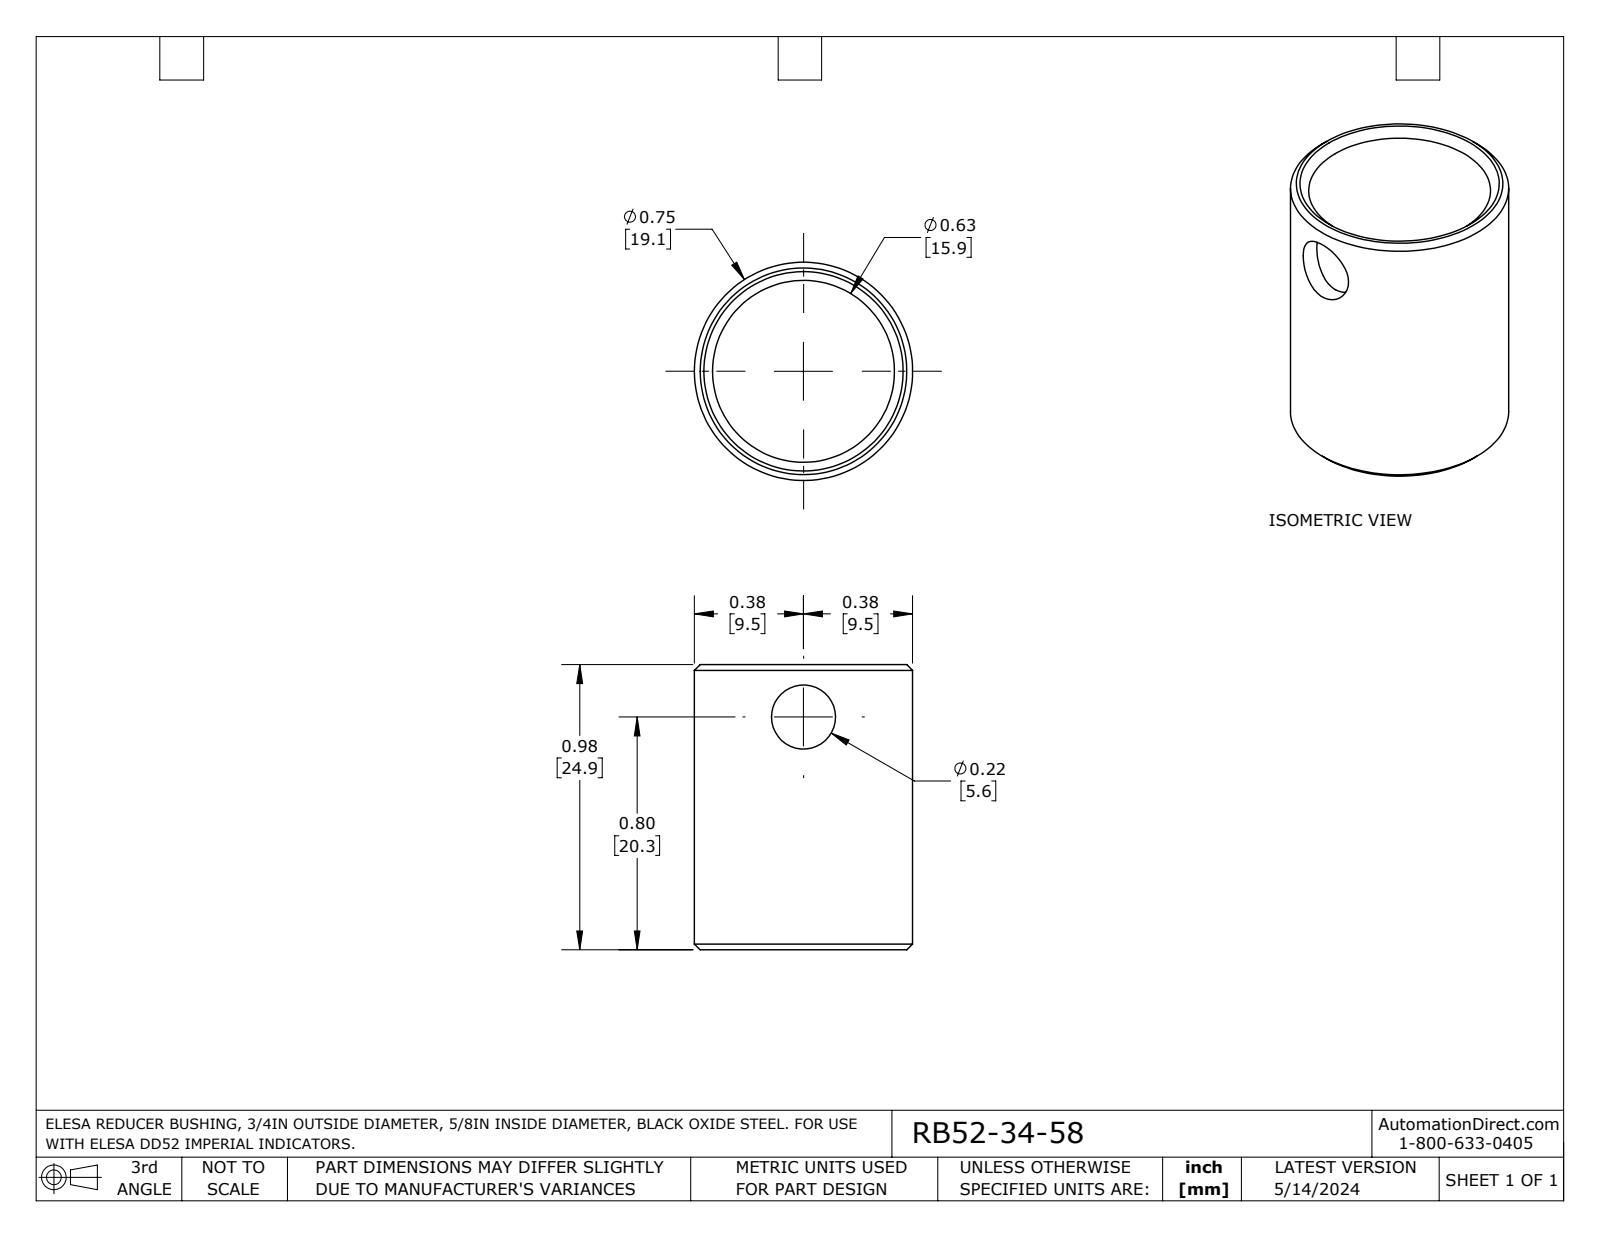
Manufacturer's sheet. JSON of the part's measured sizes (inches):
{"part_name": "RB52 3_4-5_8", "step_written_by": "SolidWorks 2023 (AUTOMOTIVE_DESIGN)", "units": "inches", "bodies": {"solids": 1, "faces": 11, "planar": 2, "cylindrical": 3, "other": 6}, "overall_size": [0.98, 0.75, 0.75], "volume_in3": 0.127, "surface_area_in2": 4.348, "round_holes": [[0.22, 1], [0.625, 1]], "round_bosses_or_shafts": [[0.75, 1]], "face_to_face_distances": [0.98]}
